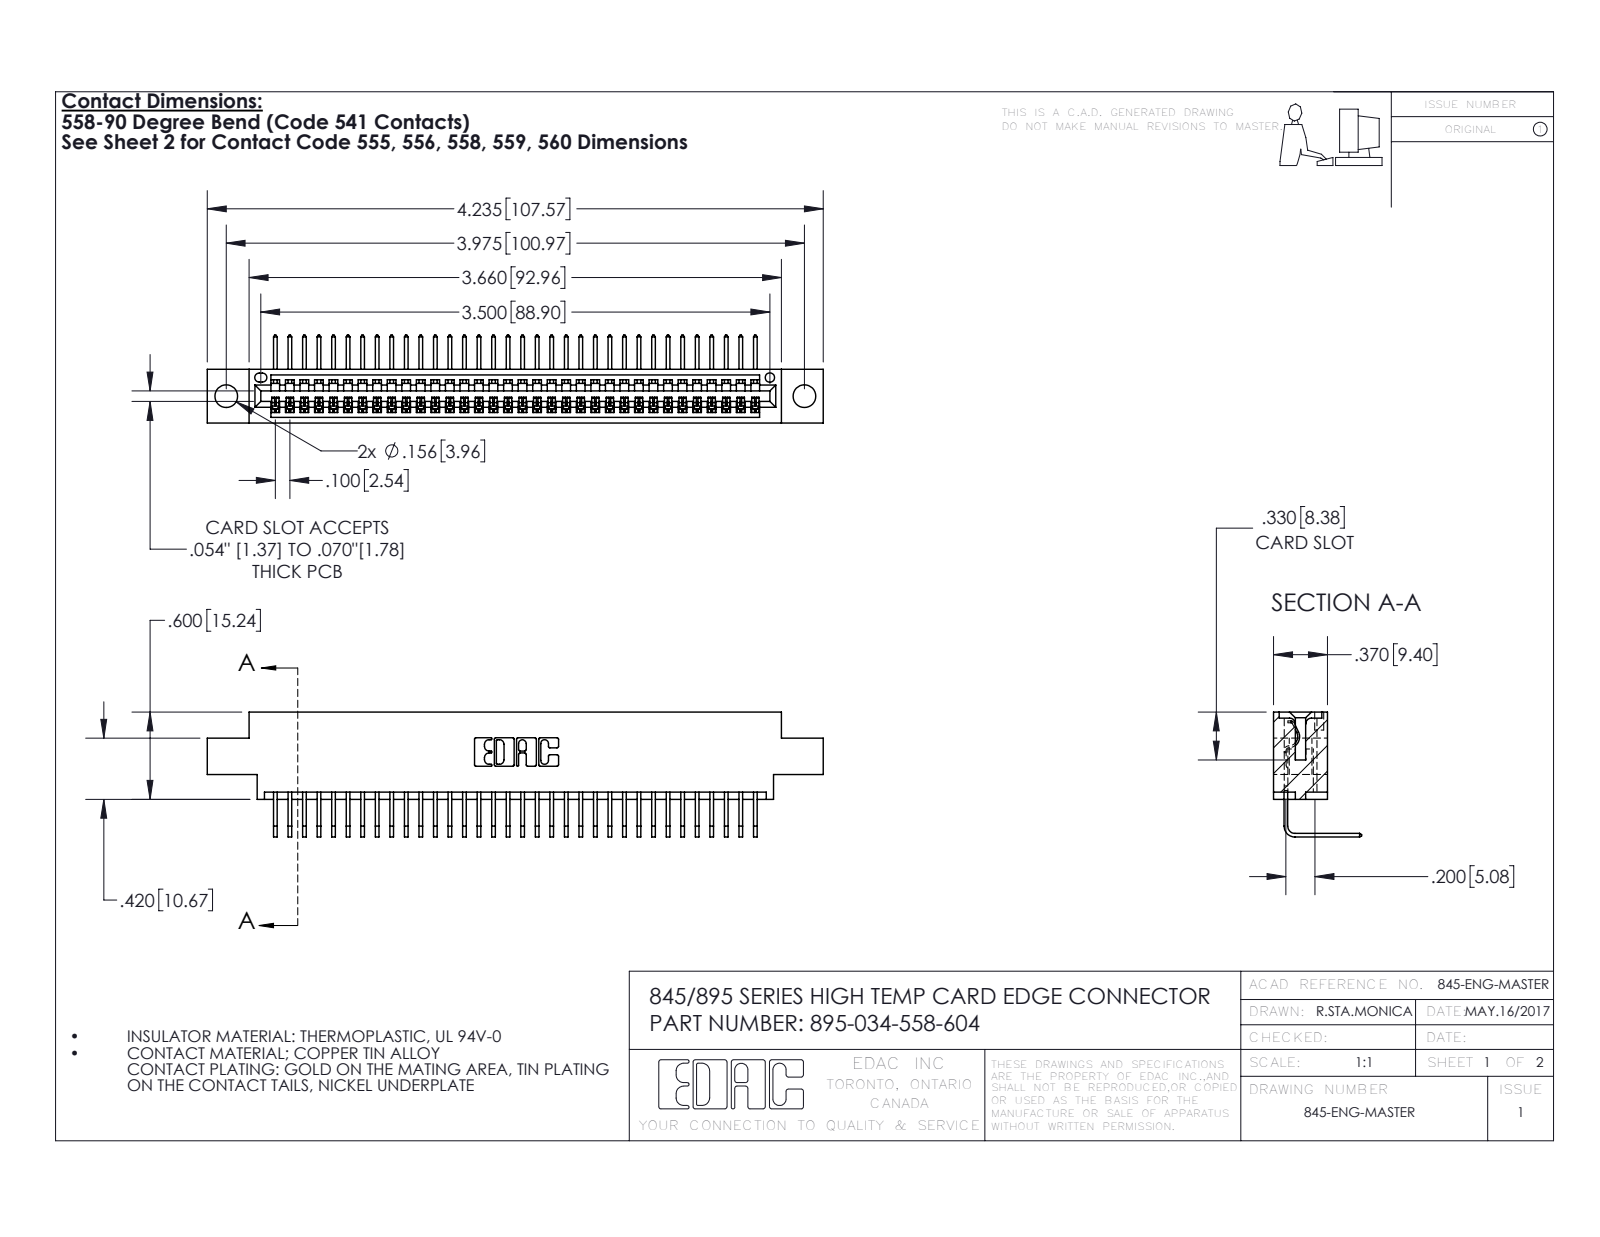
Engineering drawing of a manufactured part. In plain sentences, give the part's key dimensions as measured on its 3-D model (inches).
The part is named "345-292-001_558 Tail - 2; 345 Part_0.170 Offset - 0.156 Dia-TH; 395-034-558-604". Its 3-D file was written by "SolidWorks 2016 (CONFIG_CONTROL_DESIGN)". It is 35 solids with 2170 faces: 1512 planar, 658 cylindrical and 0 other. Overall it measures 4.235 by 0.859 by 0.605 inches. Its volume is 0.614 cubic inches and its surface area 21.49 square inches. Round holes: 2 of diameter 0.156, 1 of diameter 0.064. Partial cylindrical surfaces (rounded edges, fillets, slot ends): 68 of radius 0.006, 22 of radius 0.01, 6 of radius 0.007, 6 of radius 0.031, 3 of radius 0.026, 2 of radius 0.031, 2 of radius 0.04, 1 of radius 0.014. The main face-to-face distances are 0.072, 0.298, 0.37, 0.2, 0.098, 0.272, 0.025, 0.225, 0.175, 0.149. The hole center spacings are 0.27, 3.74, 3.975.
